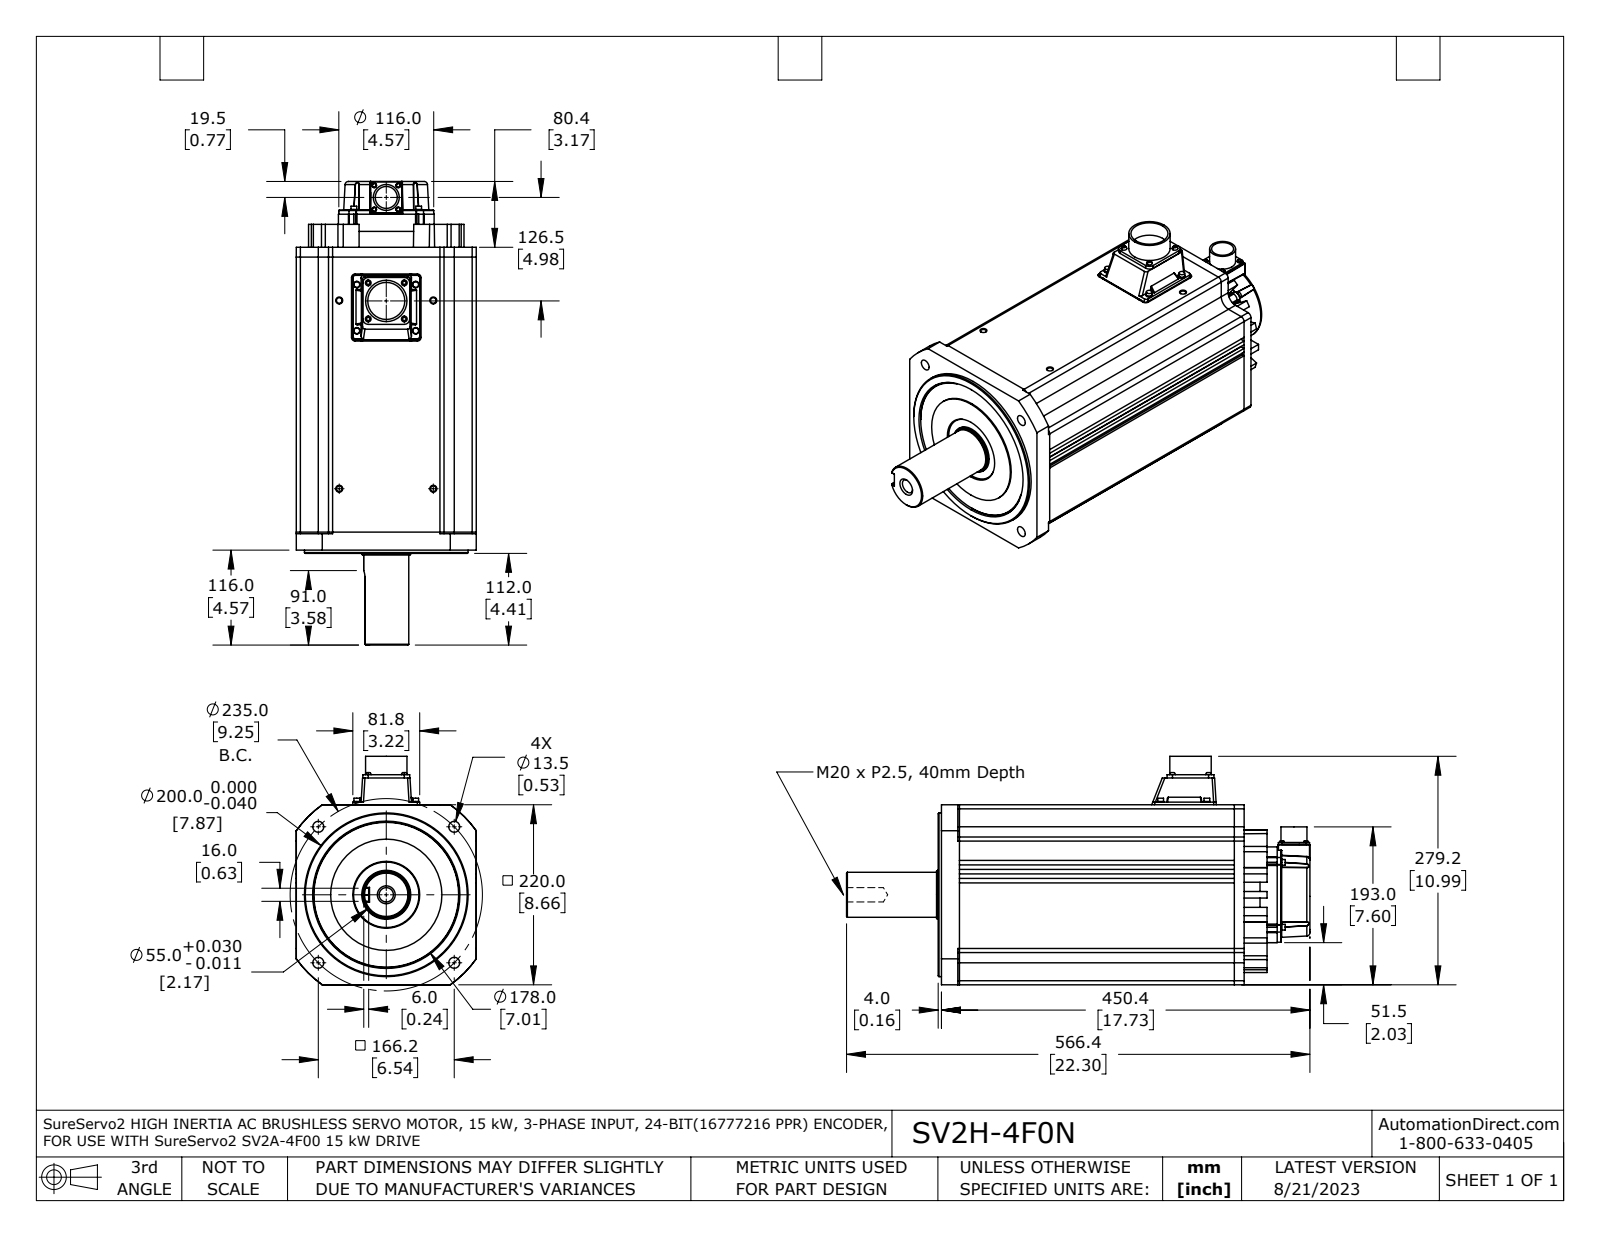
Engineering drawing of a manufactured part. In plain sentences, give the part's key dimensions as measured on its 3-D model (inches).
The part is named "SV2H-4F0N fxt r1". Its 3-D file was written by "SolidWorks 2021 (AUTOMOTIVE_DESIGN)". It is 1 solid with 734 faces: 315 planar, 212 cylindrical and 207 other. Overall it measures 22.303 by 10.992 by 8.661 inches. Its volume is 1 040 cubic inches and its surface area 902.6 square inches. Round holes: 4 of diameter 0.169, 4 of diameter 0.181, 4 of diameter 0.268, 4 of diameter 0.531, 1 of diameter 0.689, 1 of diameter 1.058, 1 of diameter 1.783, 1 of diameter 7.087. Round bosses or shafts: 8 of diameter 0.315, 8 of diameter 0.276, 4 of diameter 0.157, 1 of diameter 7.874, 1 of diameter 7.008, 1 of diameter 5.354, 1 of diameter 4.603, 1 of diameter 2.355. Partial cylindrical surfaces (rounded edges, fillets, slot ends): 24 of radius 0.118, 23 of radius 0.02, 20 of radius 0.197, 8 of radius 0.157, 4 of radius 0.039, 4 of radius 0.177, 4 of radius 0.235, 4 of radius 0.26. The main face-to-face distances are 8.661, 1.551, 7.11, 0.217, 5.559, 0.433, 0.157, 0.65, 0.315, 14.724. The hole center spacings are 4.626, 6.543, 1.141, 1.621, 1.687, 2.019, 2.224, 2.264.
